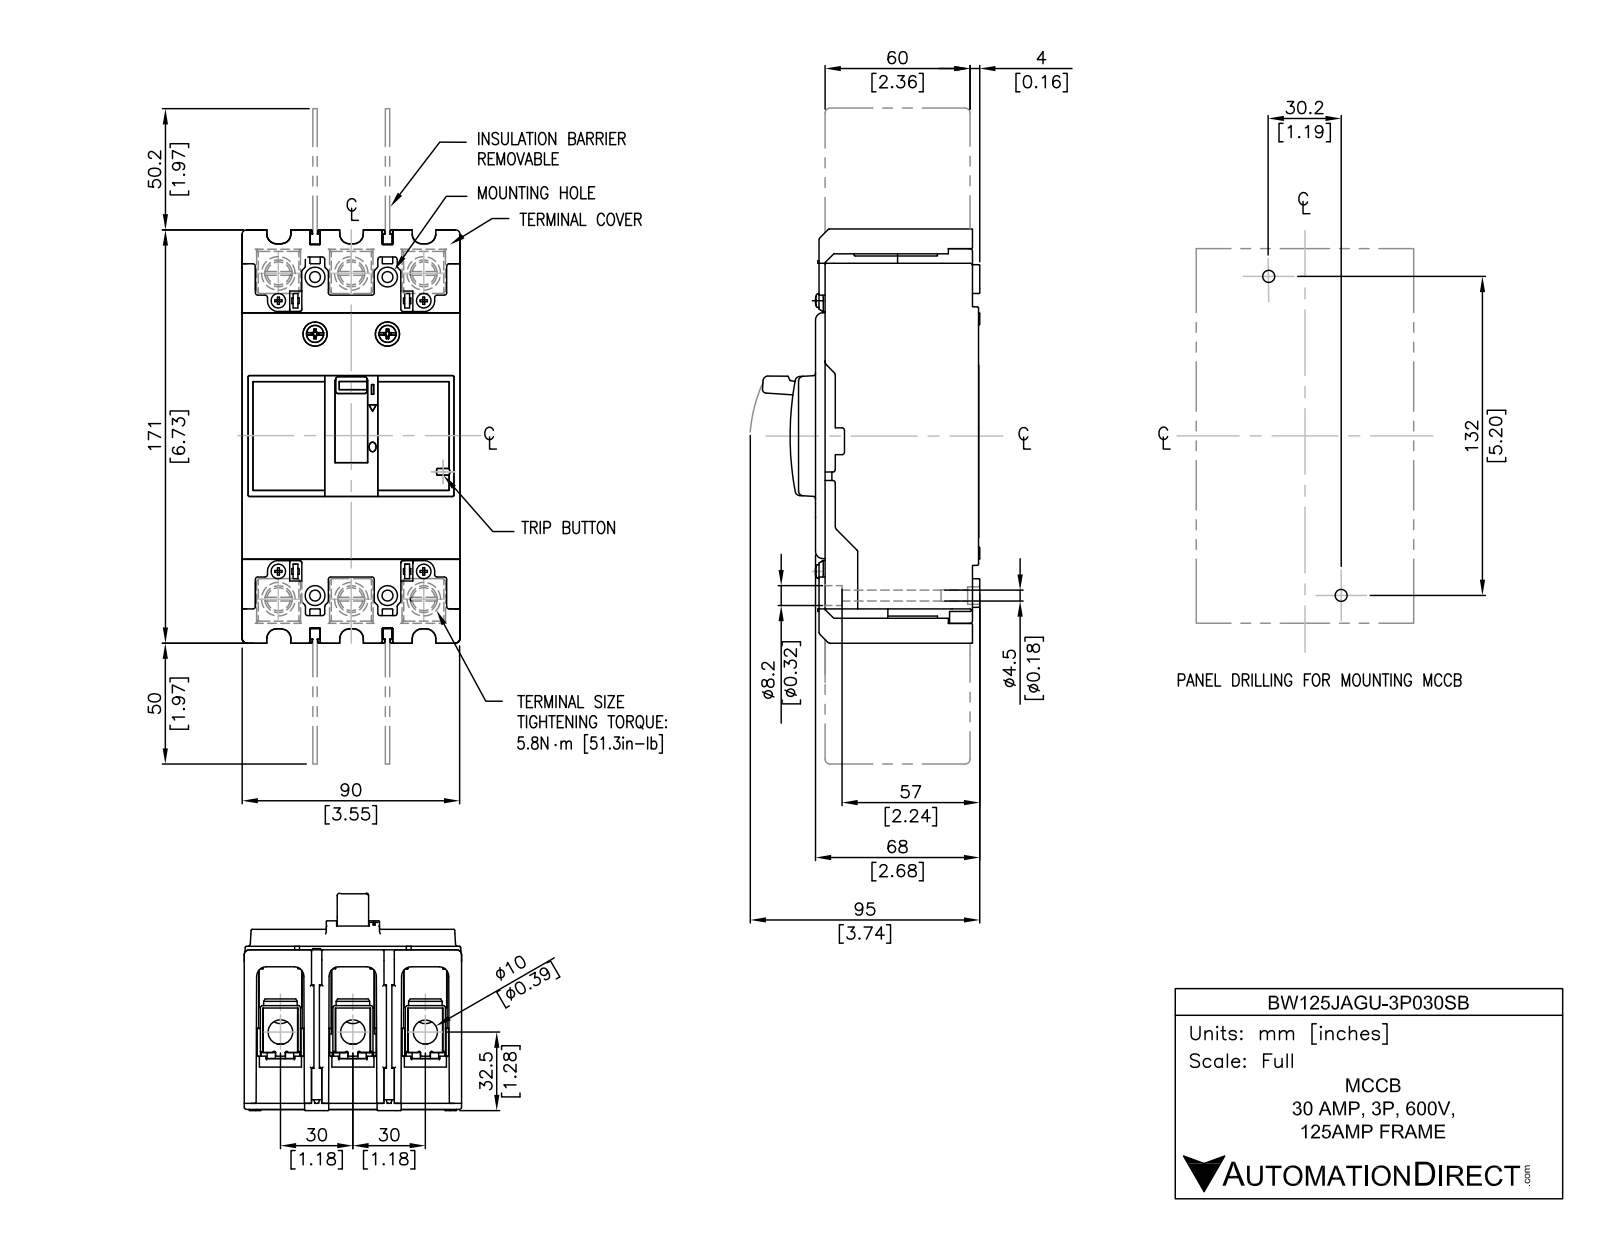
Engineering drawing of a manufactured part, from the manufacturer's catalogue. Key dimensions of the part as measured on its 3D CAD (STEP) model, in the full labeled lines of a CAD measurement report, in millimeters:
Part name (STEP PRODUCT): BW125JAGU-3P030SB
STEP written by: SolidWorks 2018 (AUTOMOTIVE_DESIGN)
Units: millimetres
Bodies: 14 solids, 452 faces (340 planar, 88 cylindrical, 24 other)
Overall size (bounding box): 259 × 91.5 × 90
Volume: 940 600 mm³ · Surface area: 148 600 mm²
Round holes (diameter × count): ⌀8 ×6, ⌀4.5 ×4, ⌀8.2 ×4
Round bosses / shafts (diameter × count): ⌀12 ×6
Partial cylindrical surfaces — rounded edges, fillets, slot ends (radius × count): R4 ×12, R2 ×6, R3 ×6
Main face-to-face distances: 30, 28.2, 31.8, 58.2, 61.8, 3.6, 90, 6, 61, 26.4
Hole centre spacings: 15.1, 134.3, 30, 45, 138.3, 140.9, 135, 60
